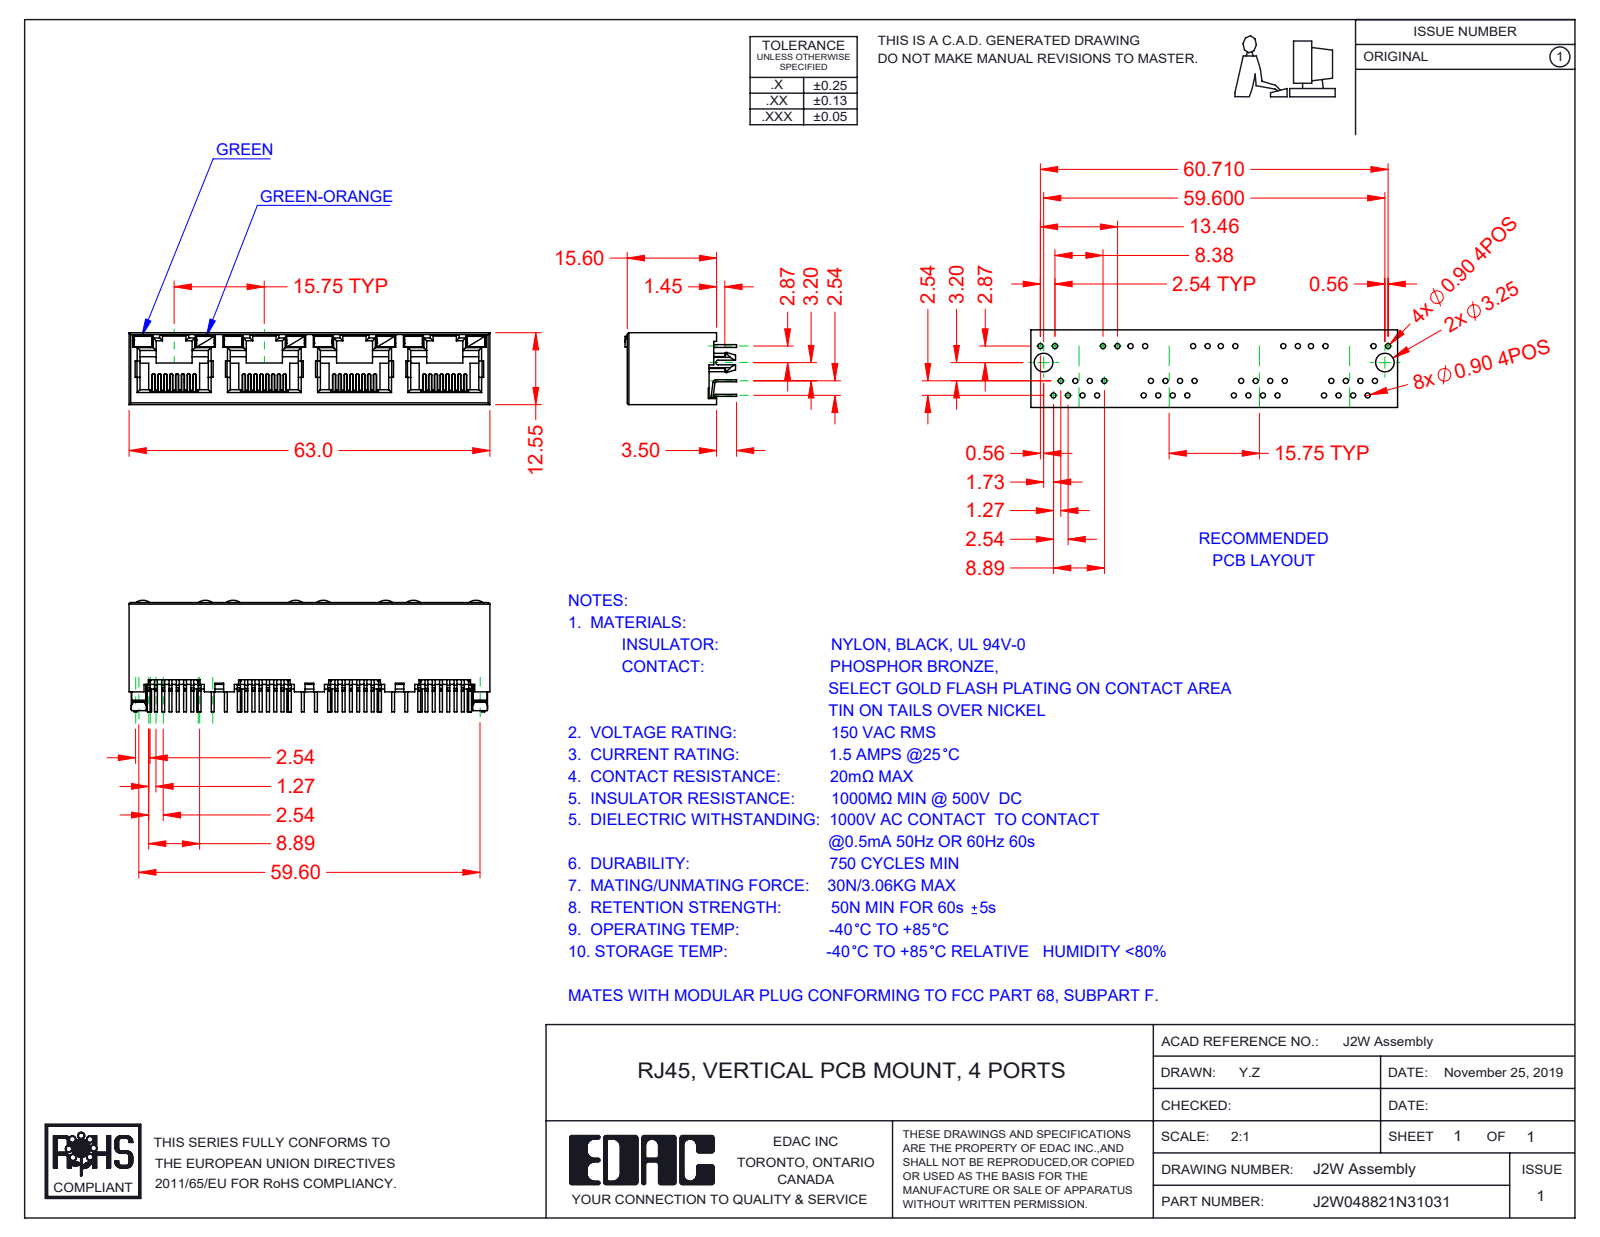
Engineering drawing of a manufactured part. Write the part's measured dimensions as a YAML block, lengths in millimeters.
part_name: "2W Contacts; 2W LED RH_7-Green-Orange; J2W048821N37131; 2W LED LH_3-Green (+2 more)"
step_written_by: "SolidWorks 2016 (CONFIG_CONTROL_DESIGN)"
units: millimeters
bodies: {solids: 45, faces: 3139, planar: 2600, cylindrical: 481, other: 58}
overall_size: [63, 19.5, 12.55]
volume: 5335
surface_area: 13144
partial_cylinders:
  - {radius: 0.15, count: 64}
  - {radius: 0.2, count: 29}
  - {radius: 0.5, count: 28}
  - {radius: 0.3, count: 14}
  - {radius: 0.45, count: 8}
  - {radius: 2, count: 8}
  - {radius: 0.25, count: 2}
  - {radius: 1.5, count: 2}
face_to_face_distances: [12.55, 11.9, 0.65, 15.75, 0.36, 1.5, 0.78, 0.6, 11.3, 31.5]
